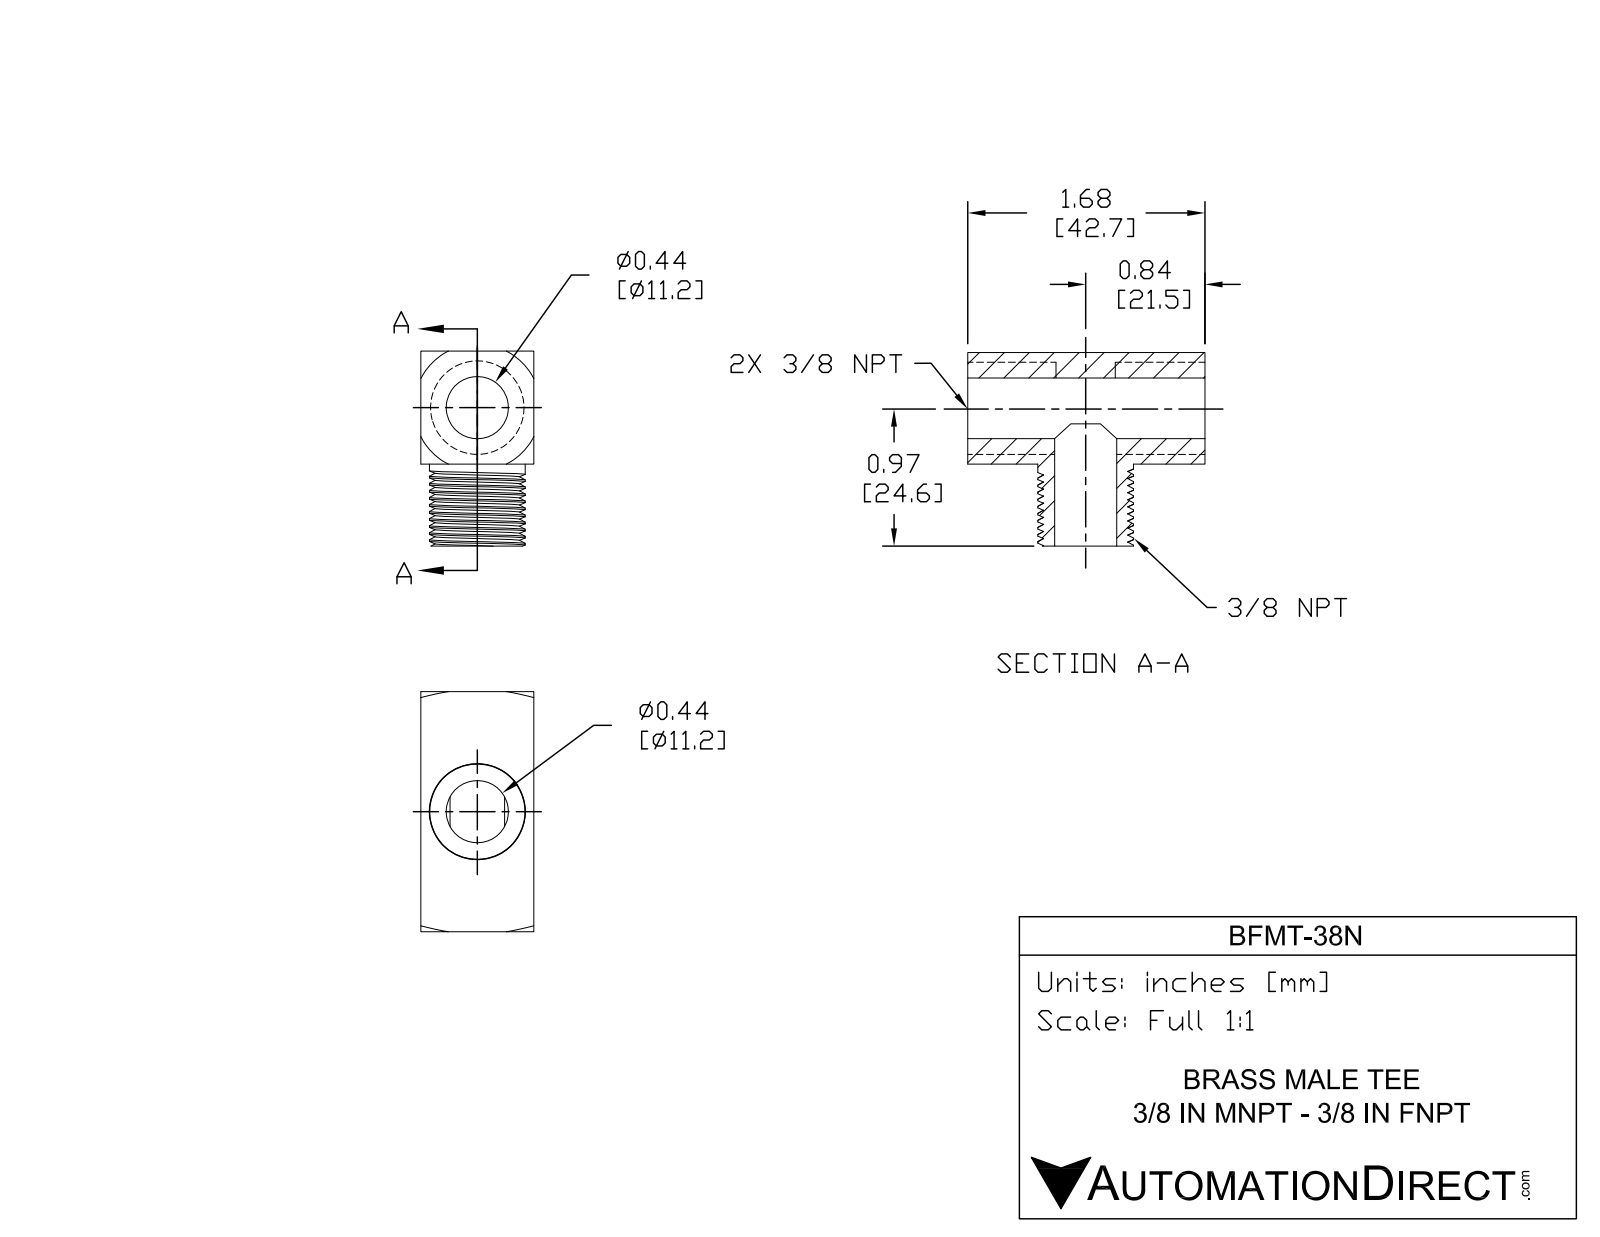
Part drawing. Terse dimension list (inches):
name: BFMT-38N
written by: SolidWorks 2015 (CONFIG_CONTROL_DESIGN)
unit: in
bodies: 1 solid, 47 faces (10 planar, 27 cylindrical, 10 other)
size: 1.7 × 1.38 × 0.8
volume: 0.9 in³; area: 11.78 in²
holes: 2× ⌀0.44
bosses: 1× ⌀0.678
face distances: 0.8, 1.7, 1.38, 0.58, 0.505, 0.295, 0.875, 0.85
